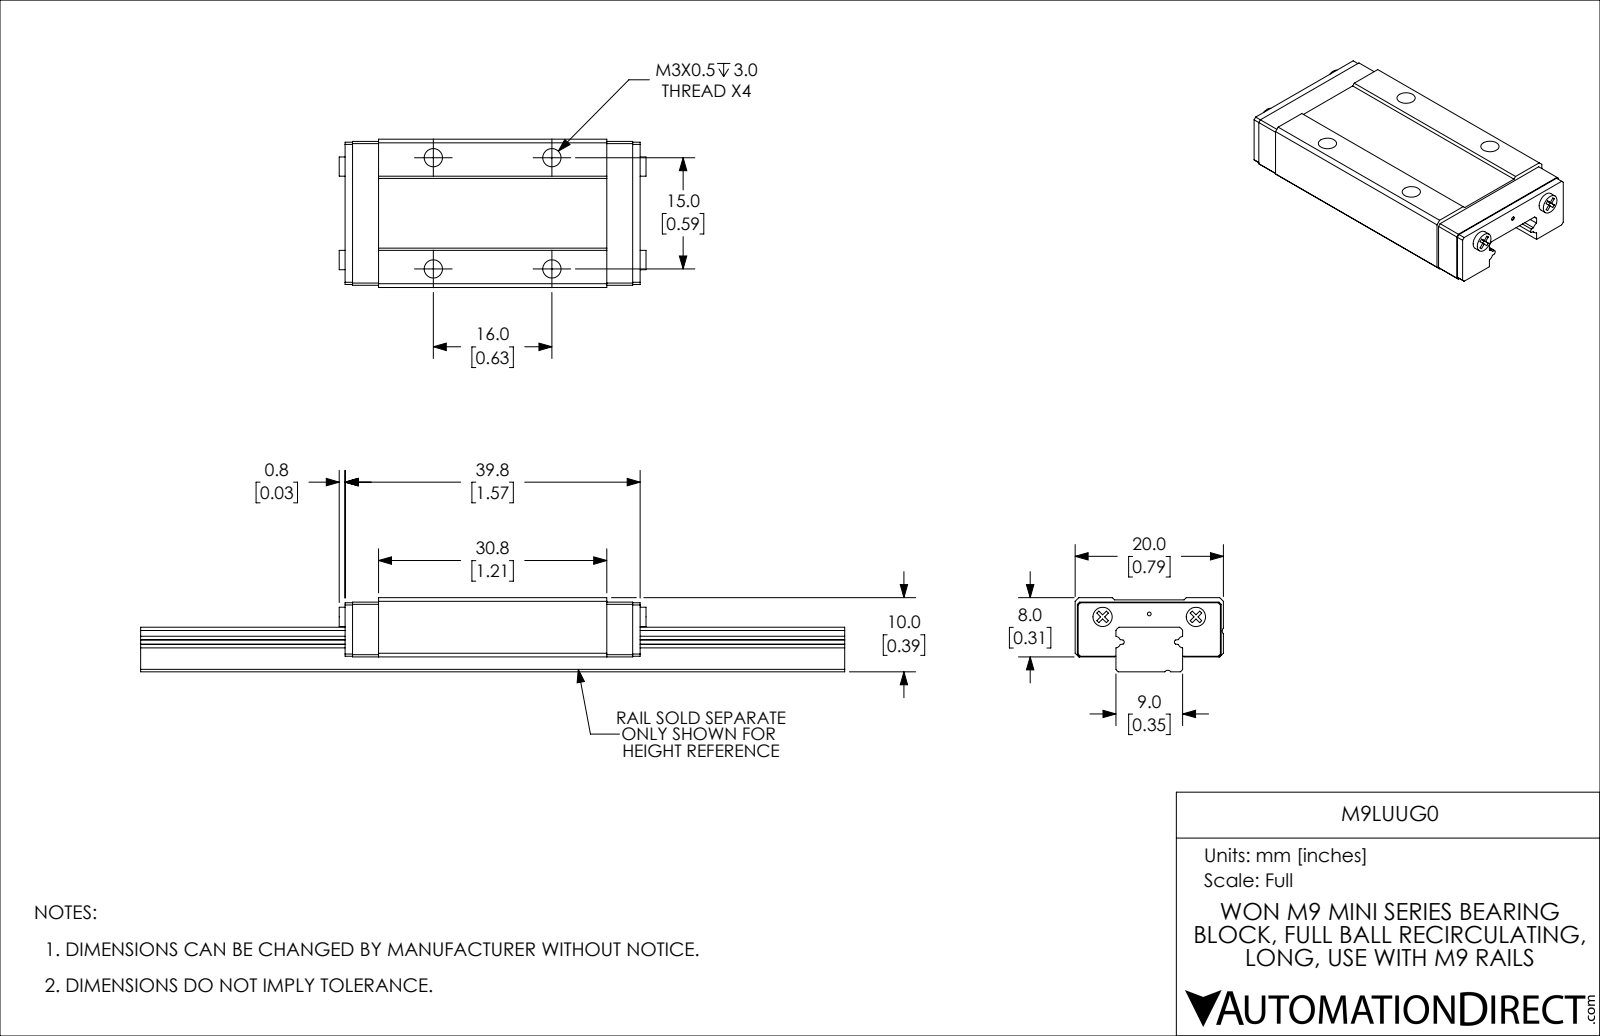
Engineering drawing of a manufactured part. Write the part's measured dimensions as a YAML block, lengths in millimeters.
part_name: "M9LUUG0"
step_written_by: "SolidWorks 2019 (CONFIG_CONTROL_DESIGN)"
units: millimeters
bodies: {solids: 1, faces: 156, planar: 119, cylindrical: 29, other: 8}
overall_size: [41.4, 20, 8]
volume: 4706
surface_area: 2975
round_holes:
  - {diameter: 2.46, count: 4}
  - {diameter: 0.5, count: 1}
round_bosses_or_shafts:
  - {diameter: 2.6, count: 2}
partial_cylinders:
  - {radius: 0.32, count: 2}
  - {radius: 0.8, count: 2}
  - {radius: 0.95, count: 2}
  - {radius: 0.6, count: 1}
face_to_face_distances: [4, 7.7, 3.7, 8, 20, 5.5, 14.5, 7.4, 3.4, 0.6]
hole_center_spacings: [15, 16, 21.93]
